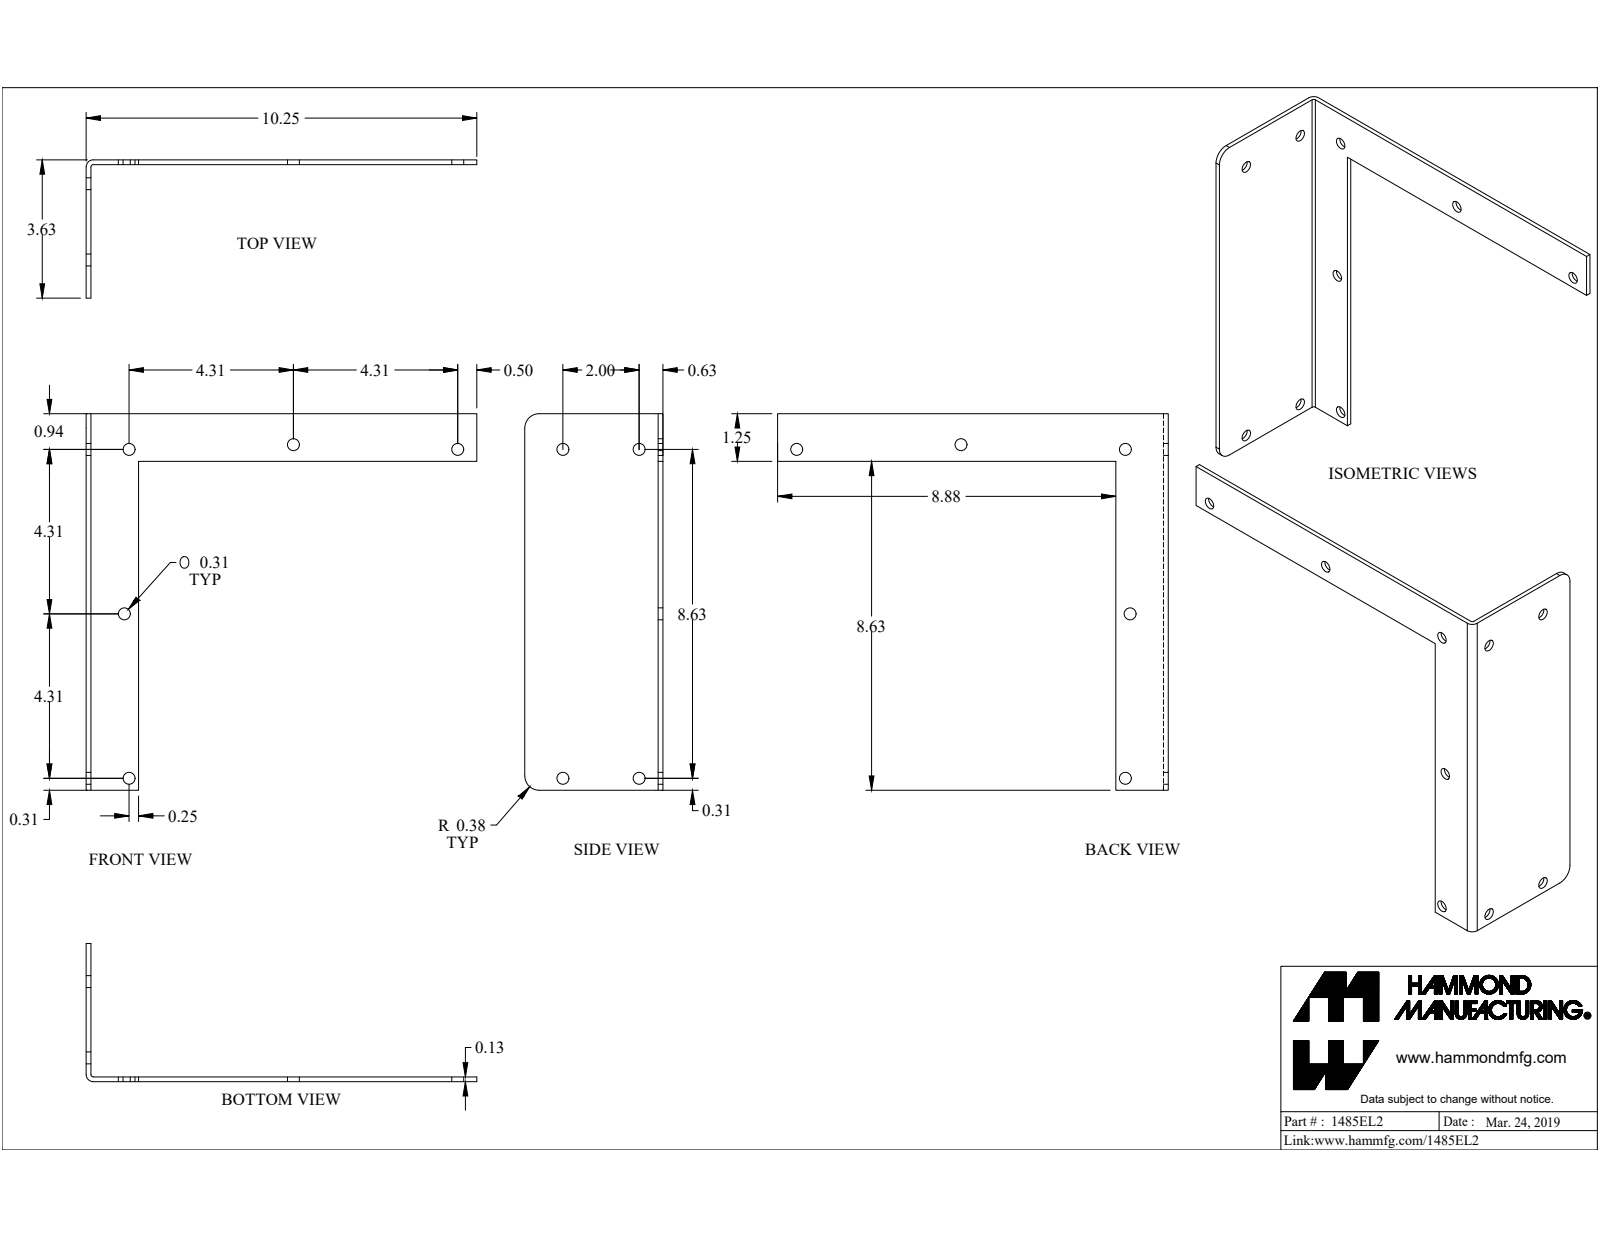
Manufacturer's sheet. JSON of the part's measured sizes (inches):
{"part_name": "1485EL2", "step_written_by": "SolidWorks 2019 (CONFIG_CONTROL_DESIGN)", "units": "inches", "bodies": {"solids": 1, "faces": 23, "planar": 10, "cylindrical": 13, "other": 0}, "overall_size": [10.25, 9.875, 3.625], "volume_in3": 7.246, "surface_area_in2": 122.9, "round_holes": [[0.313, 9]], "partial_cylinders_radius": [[0.375, 2], [0.06, 1], [0.185, 1]], "face_to_face_distances": [0.125, 3.5, 3.625, 1.25, 1.375, 1.25, 9.875, 8.625, 10.25, 10.125], "hole_center_spacings": [8.625, 2, 8.854, 4.313, 4.314, 4.315, 4.315, 6.274]}
